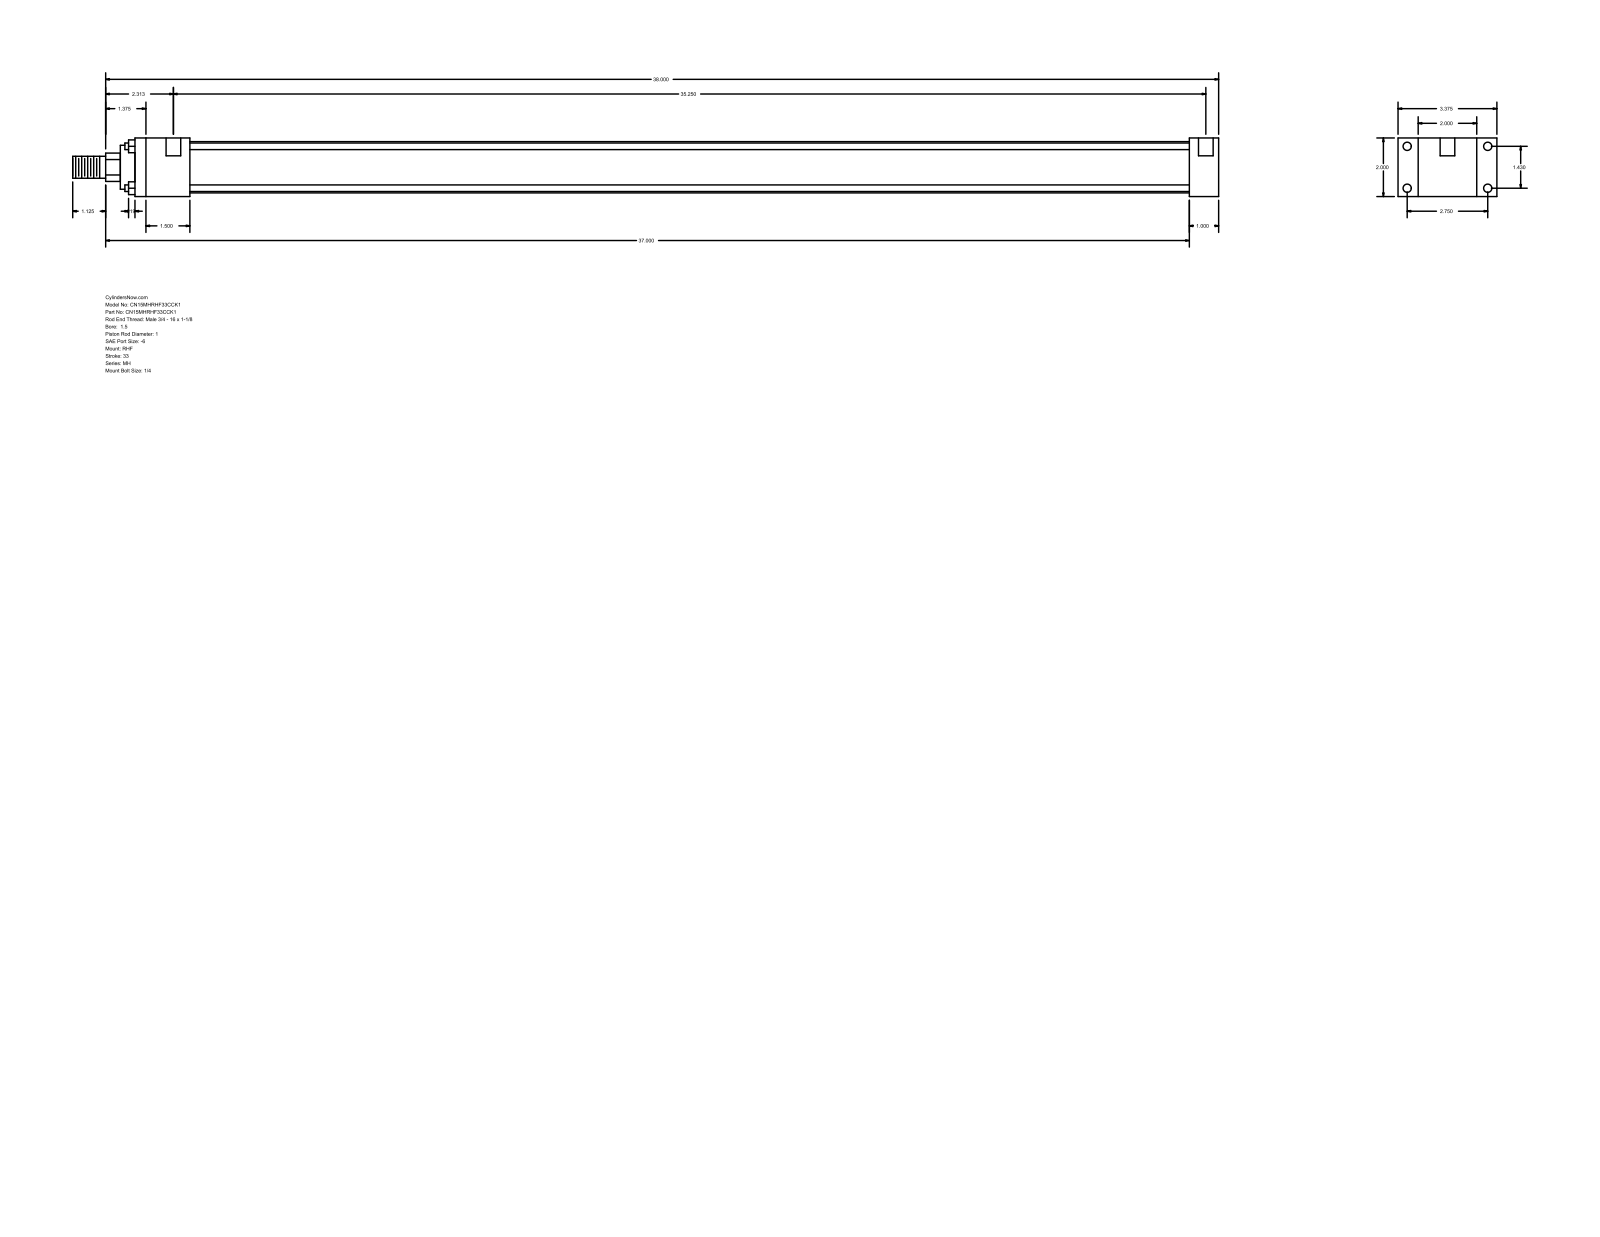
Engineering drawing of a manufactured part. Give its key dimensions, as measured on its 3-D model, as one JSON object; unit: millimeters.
{"part_name": "MH_RHF__0150_1", "step_written_by": "GSSL Pune (CONFIG_CONTROL_DESIGN)", "units": "millimeters", "bodies": {"solids": 0, "faces": 88, "planar": 60, "cylindrical": 28, "other": 0}, "overall_size": [993.77, 85.72, 50.8], "round_holes": [[5.56, 4], [7.14, 4], [12.7, 2]], "round_bosses_or_shafts": [[5.71, 4], [44.45, 1], [38.1, 1], [25.4, 1], [19.05, 1]], "partial_cylinders_radius": [[12.29, 1]], "face_to_face_distances": [50.8, 25.4, 17.46, 68.26, 85.72, 939.8, 914.4, 47.63, 866.77, 892.17], "hole_center_spacings": [36.32, 69.84, 78.72, 898.53, 3.18, 895.35]}
